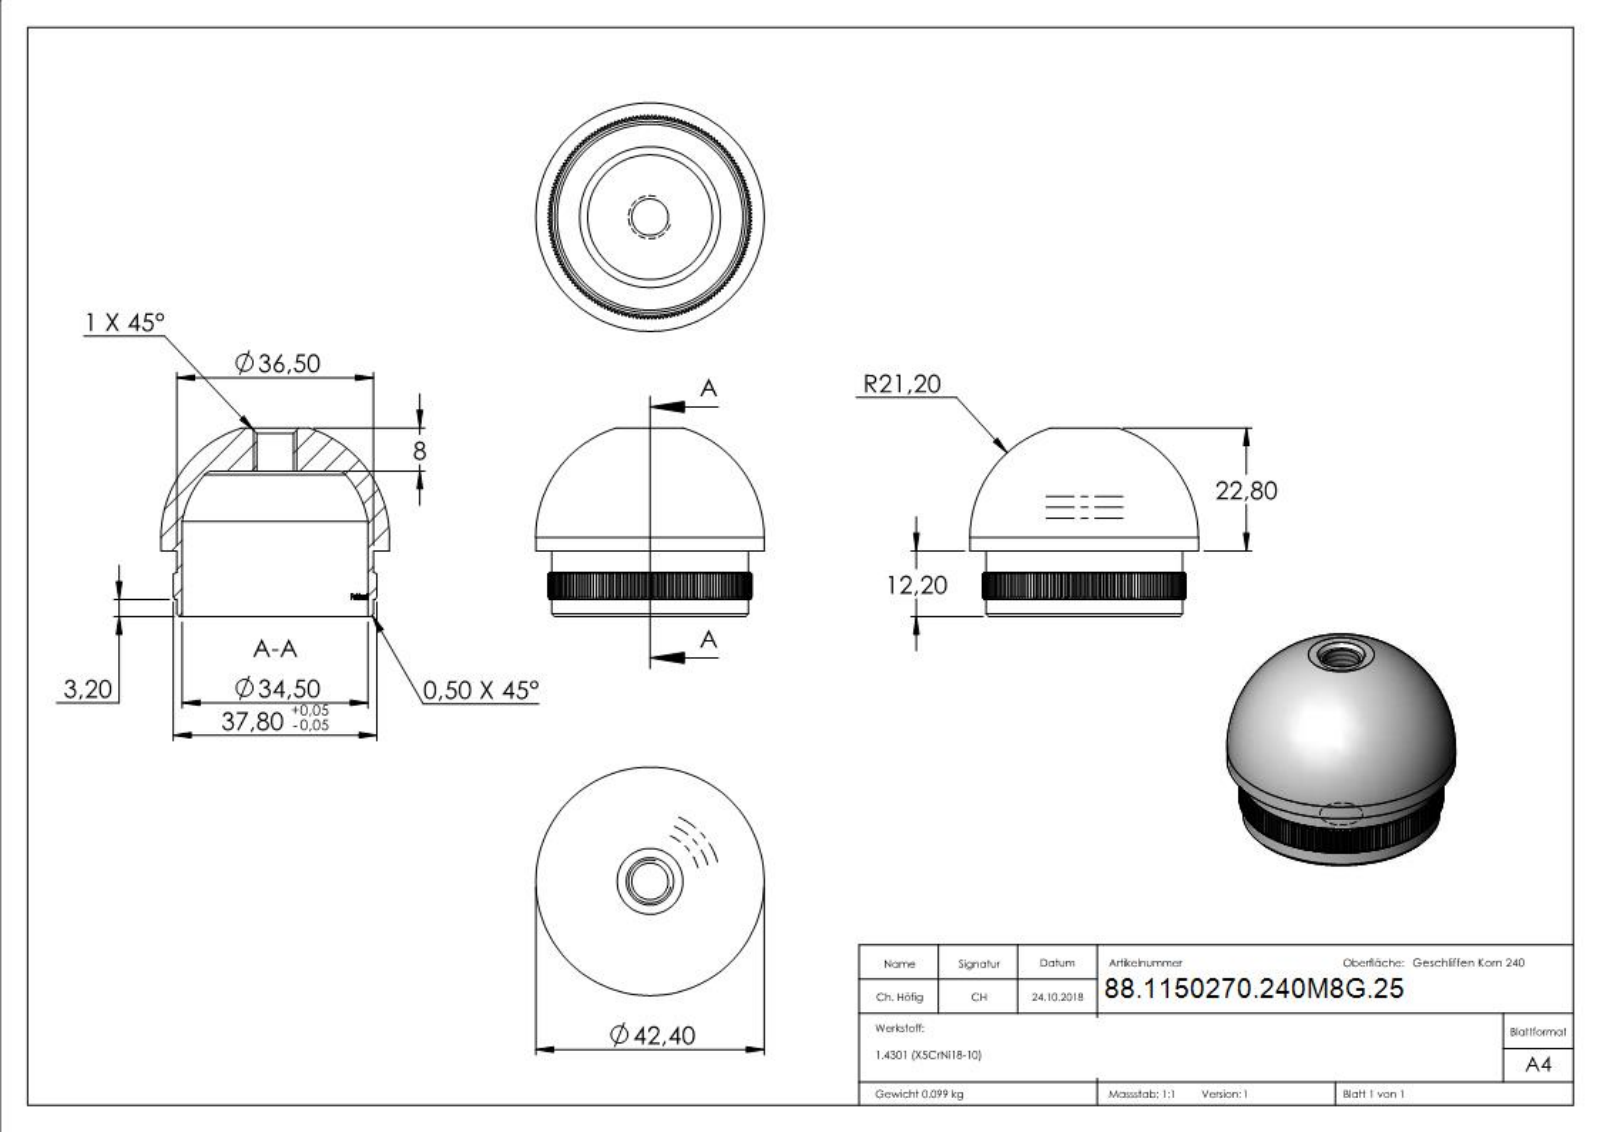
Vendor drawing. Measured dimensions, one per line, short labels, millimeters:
name: 50270-240M8G-25
written by: SolidWorks 2015 (CONFIG_CONTROL_DESIGN)
unit: mm
bodies: 1 solid, 1105 faces (451 planar, 207 cylindrical, 447 other)
size: 42.4 × 42.4 × 35
volume: 12 566 mm³; area: 9 070 mm²
holes: 1× ⌀6.8, 1× ⌀34.5
bosses: 1× ⌀42.4, 1× ⌀36.5
rounds: 1× R17.35, 1× R18.9
face distances: 14.8, 18.4, 18.42, 18.38, 8, 22.8, 12.2, 27, 35, 3.2
